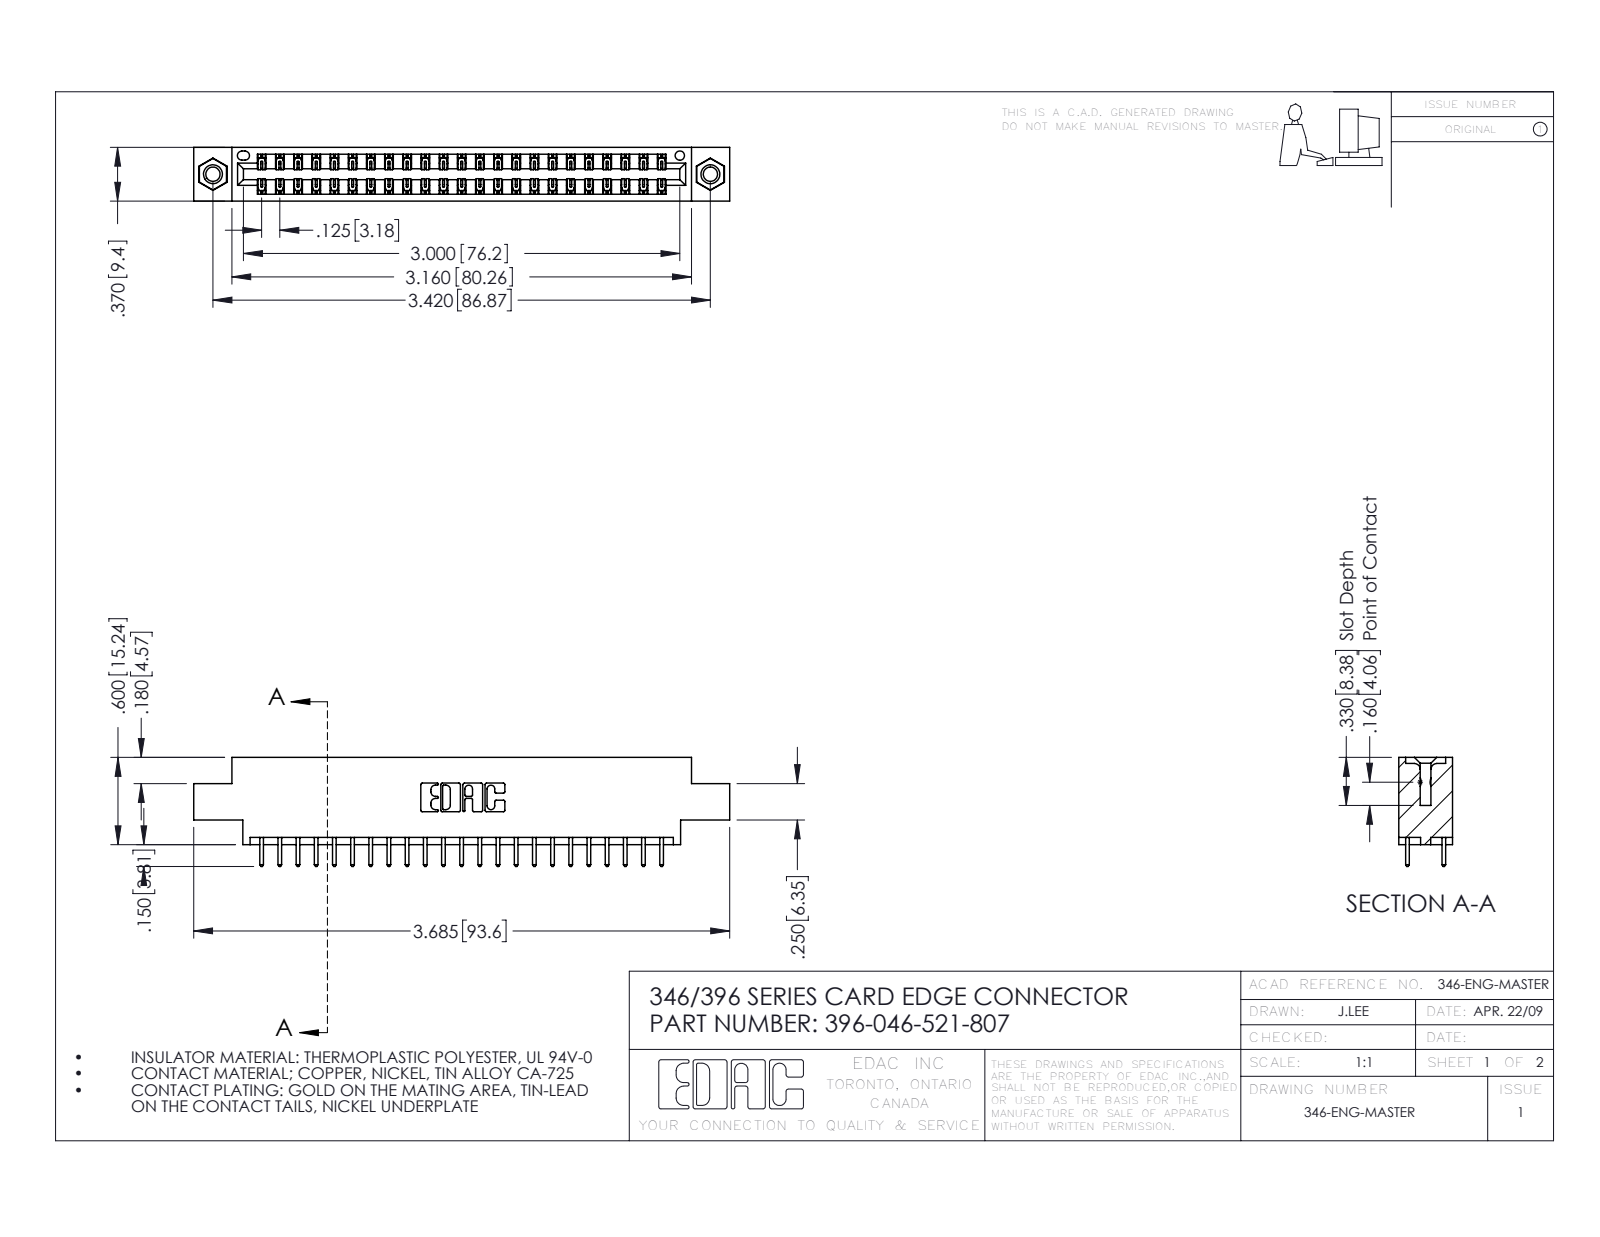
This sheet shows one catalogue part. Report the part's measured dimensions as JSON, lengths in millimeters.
{"part_name": "345-292-001_345-293-121; 396-046-521-807; 345-250-001_345-250-005-103; 346 Part_0.170 Offset - 0.156 Dia-TI", "step_written_by": "SolidWorks 2016 (CONFIG_CONTROL_DESIGN)", "units": "millimeters", "bodies": {"solids": 49, "faces": 2578, "planar": 1722, "cylindrical": 840, "other": 16}, "overall_size": [93.6, 19.1, 9.4], "volume_mm3": 8800, "surface_area_mm2": 11880, "round_holes": [[2.5, 2], [3.2, 2], [4, 2], [1.6, 1]], "round_bosses_or_shafts": [[3.9, 2]], "partial_cylinders_radius": [[0.2, 69], [0.3, 46], [0.3, 22], [0.2, 6], [0.8, 6], [0.7, 3], [0.4, 2], [0.6, 2]], "face_to_face_distances": [1.2, 8.2, 9.4, 6.4, 1.8, 7.6, 0.6, 7, 5.6, 3.8], "hole_center_spacings": [6.2, 81.6, 86.9]}
